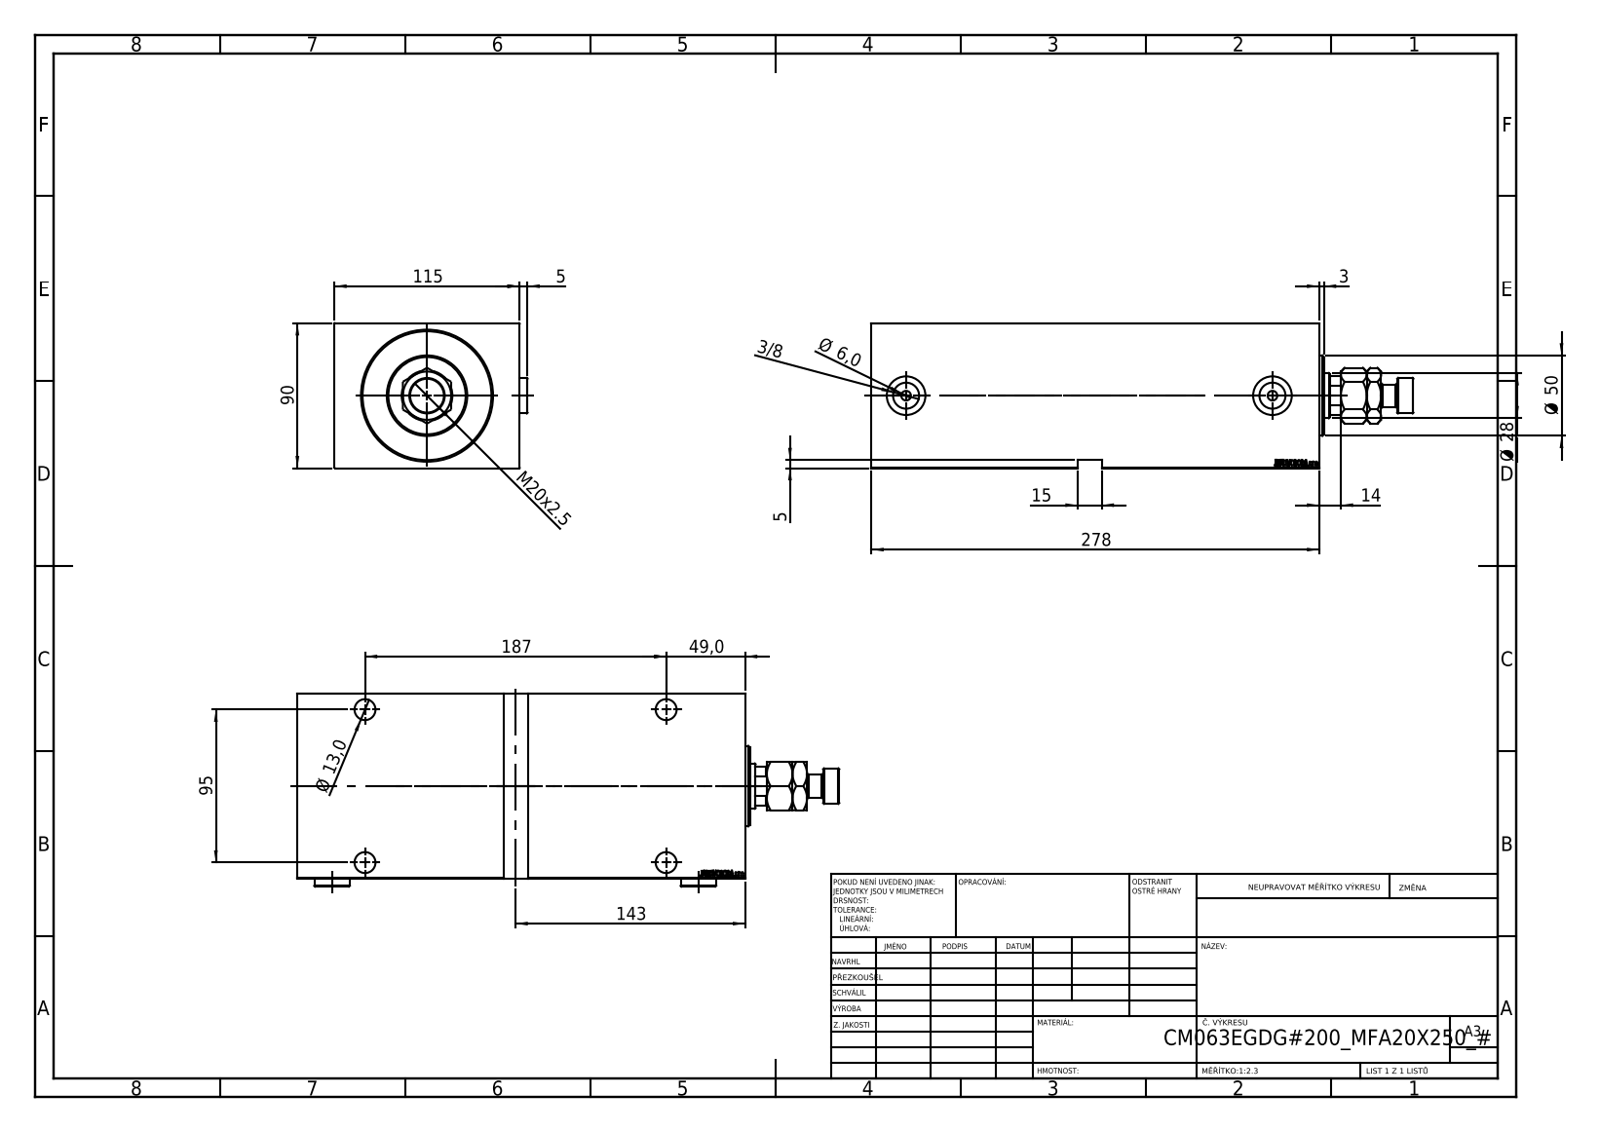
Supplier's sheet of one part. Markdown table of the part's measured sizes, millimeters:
| quantity | value |
| --- | --- |
| part name | Zatka_OIL_PORT; MFA; V450CM_E_VCP; V450CM_VC_B (+1 more) |
| STEP written by | SolidWorks 2019 (CONFIG_CONTROL_DESIGN) |
| units | millimeters |
| bodies | 6 solids, 964 faces (462 planar, 72 cylindrical, 430 other) |
| overall size | 336.5 × 119.9 × 90 |
| volume | 2 336 000 mm³ |
| surface area | 265 497 mm² |
| round holes (diameter × count) | 13 × 4, 19 × 4, 6 × 2, 16.17 × 2, 24 × 2, 18.5 × 1, 28 × 1, 31.5 × 1, 63 × 1, 80 × 1 |
| round bosses / shafts (diameter × count) | 22 × 3, 65 × 1, 50 × 1, 14 × 1 |
| partial cylindrical surfaces (radius × count) | 13.5 × 1 |
| main face-to-face distances | 90, 115, 278, 17.5, 260.5, 5, 273, 255.5, 208.5, 261.4 |
| hole center spacings | 95, 187, 209.75, 227.5 |
